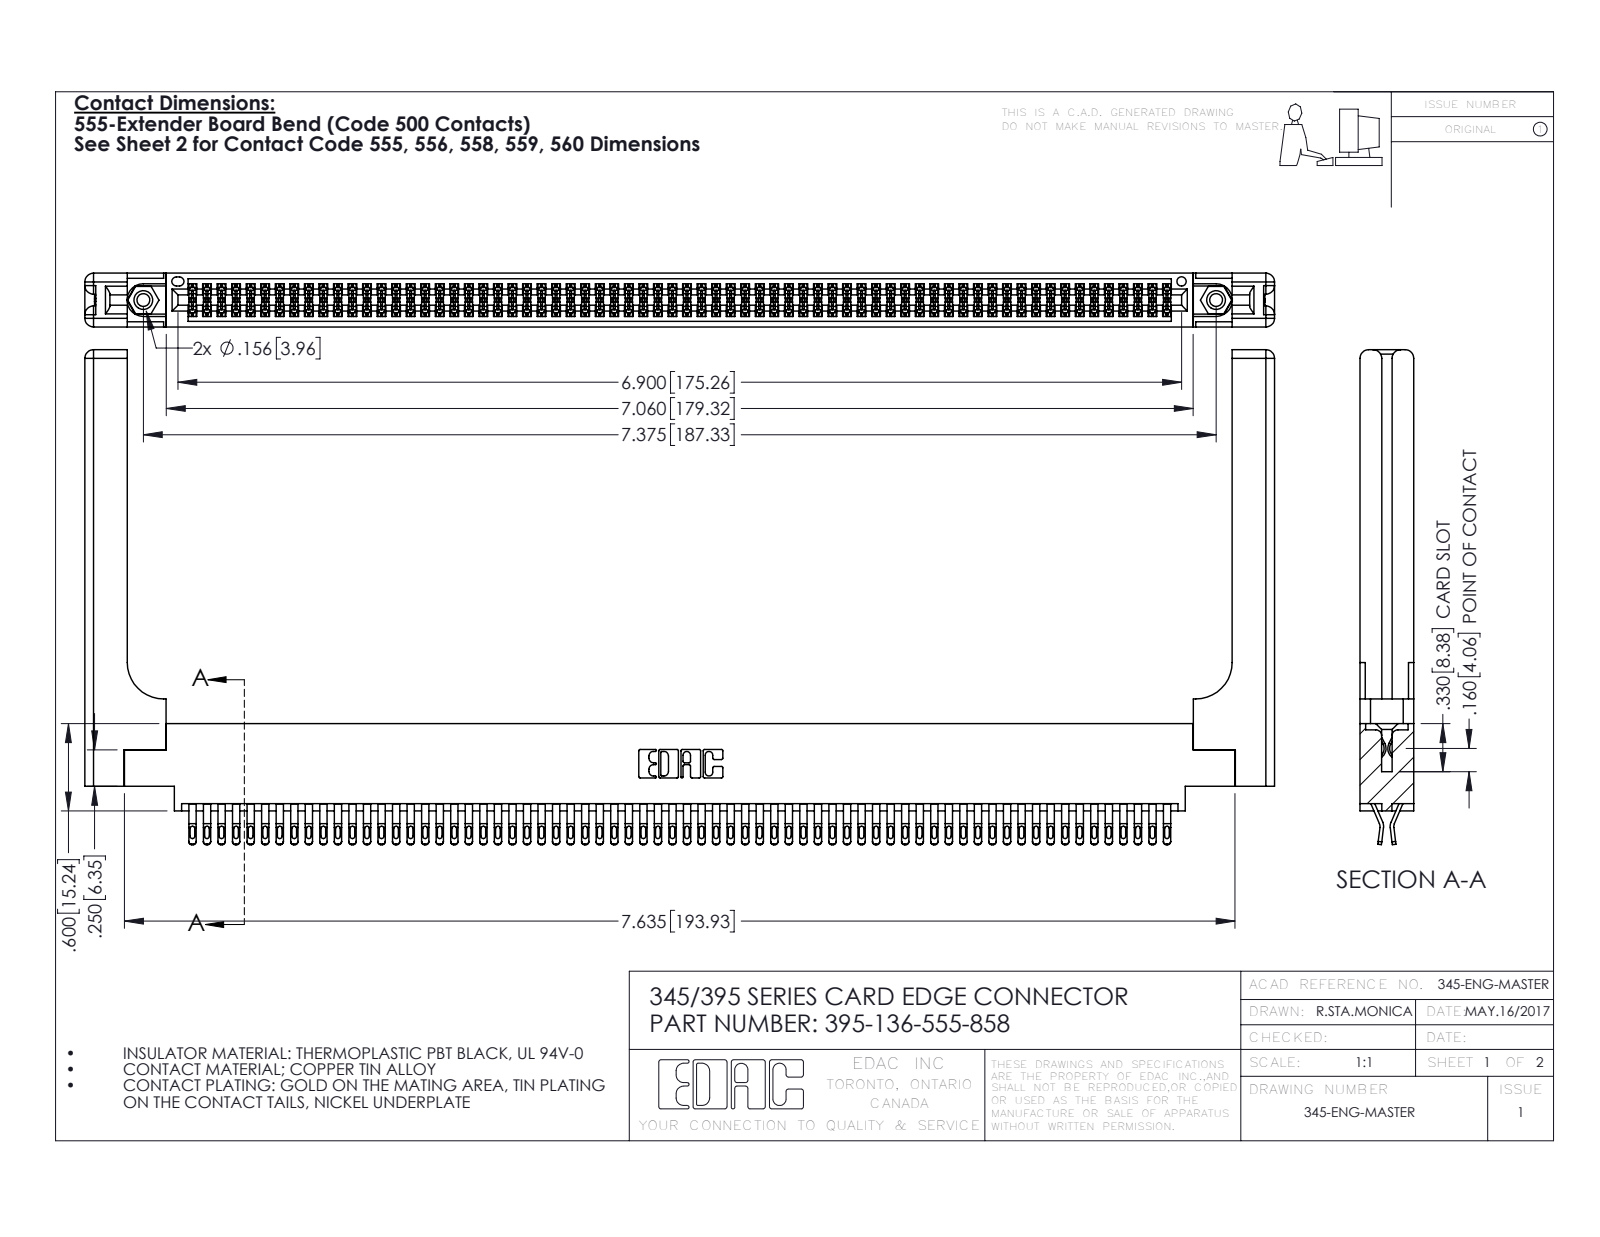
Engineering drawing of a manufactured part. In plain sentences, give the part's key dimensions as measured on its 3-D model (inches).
The part is named "345-250-001_345-250-001-102; 345-220-058_345-220-058; 345 Part_0.170 Offset - 0.156 Dia-TH; 395-136-555-858 (+1 more)". Its 3-D file was written by "SolidWorks 2016 (CONFIG_CONTROL_DESIGN)". It is 141 solids with 8002 faces: 4448 planar, 3494 cylindrical and 60 other. Overall it measures 8.179 by 3.402 by 0.37 inches. Its volume is 1.781 cubic inches and its surface area 58.41 square inches. Round holes: 2 of diameter 0.089, 2 of diameter 0.125, 2 of diameter 0.156, 1 of diameter 0.064. Round bosses or shafts: 2 of diameter 0.155. Partial cylindrical surfaces (rounded edges, fillets, slot ends): 340 of radius 0.016, 272 of radius 0.02, 204 of radius 0.006, 22 of radius 0.01, 16 of radius 0.06, 6 of radius 0.007, 6 of radius 0.031, 3 of radius 0.026. The main face-to-face distances are 0.072, 0.298, 0.37, 0.025, 0.098, 0.272, 0.2, 0.225, 0.175, 0.148. The hole center spacings are 0.27, 7.139, 7.375.
